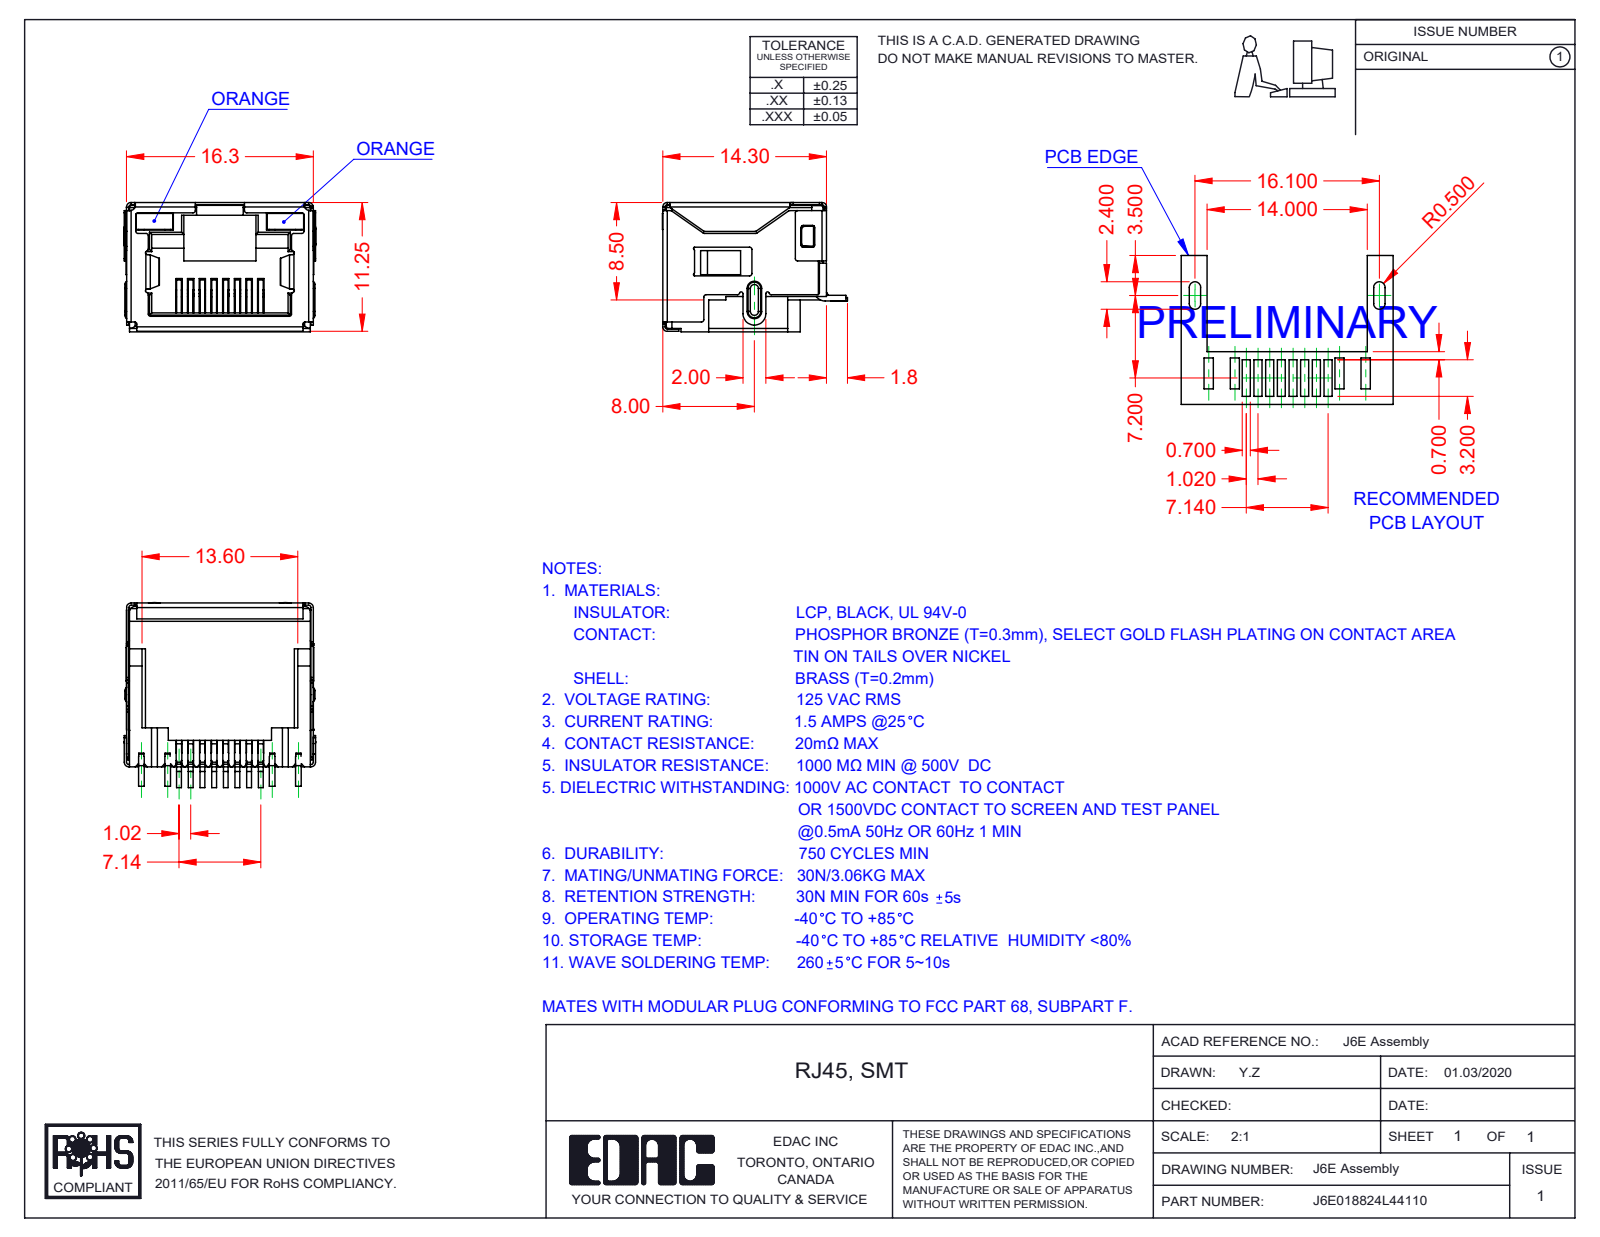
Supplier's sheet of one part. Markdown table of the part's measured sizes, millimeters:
| quantity | value |
| --- | --- |
| part name | J6E018824L44110; 6E Shield_LED; 6E Insulator_LED; 6E Contacts (+2 more) |
| STEP written by | SolidWorks 2016 (CONFIG_CONTROL_DESIGN) |
| units | millimeters |
| bodies | 12 solids, 1496 faces (1099 planar, 347 cylindrical, 50 other) |
| overall size | 16.75 × 16.15 × 11.3 |
| volume | 1 109 mm³ |
| surface area | 4 045 mm² |
| partial cylindrical surfaces (radius × count) | 0.2 × 82, 0.25 × 17, 0.4 × 13, 0.5 × 13, 0.1 × 10, 0.15 × 7, 0.3 × 4, 1 × 3 |
| main face-to-face distances | 11.05, 16.05, 16.1, 15.85, 11.1, 11.3, 2.4, 0.7, 9.85, 0.49 |
